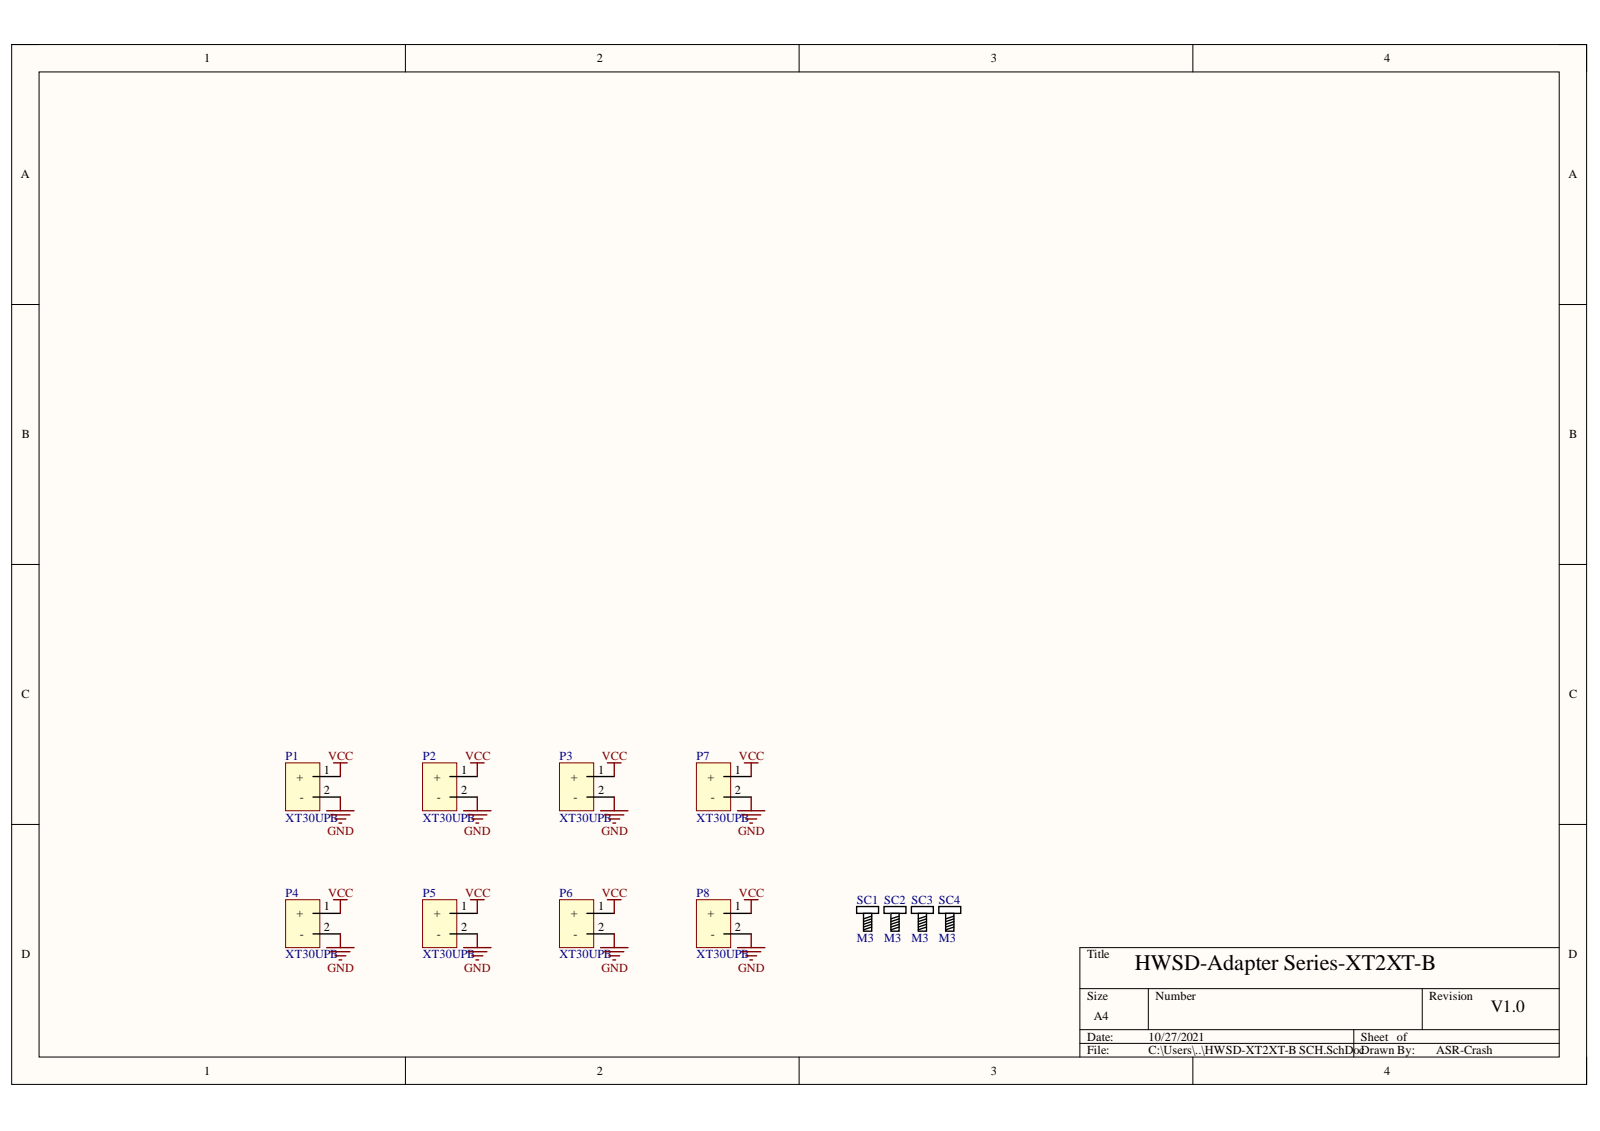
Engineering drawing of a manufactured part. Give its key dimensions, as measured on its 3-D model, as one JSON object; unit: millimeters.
{"part_name": "PCB; Board; P8; XT30UPB-F (+7 more)", "step_written_by": "Open CASCADE 6.8 (AUTOMOTIVE_DESIGN)", "units": "millimeters", "bodies": {"solids": 11, "faces": 2465, "planar": 1551, "cylindrical": 336, "other": 578}, "overall_size": [40.12, 20.12, 11.4], "volume_mm3": 3383, "surface_area_mm2": 6123, "round_holes": [[1.8, 16], [2.2, 14], [2.6, 14], [3, 4], [2.5, 2]], "round_bosses_or_shafts": [[1.6, 16]], "partial_cylinders_radius": [[0.5, 58], [0.1, 28], [1, 28], [0.2, 16], [1.5, 16], [1.8, 16], [2.54, 4]], "face_to_face_distances": [1.69, 0.6, 5.09, 0.4, 3.4, 4.6, 14.92, 4.2, 2.8, 8.8], "hole_center_spacings": [7.46, 5, 8.98, 15, 16.75, 14.92, 22.6, 27.57]}
